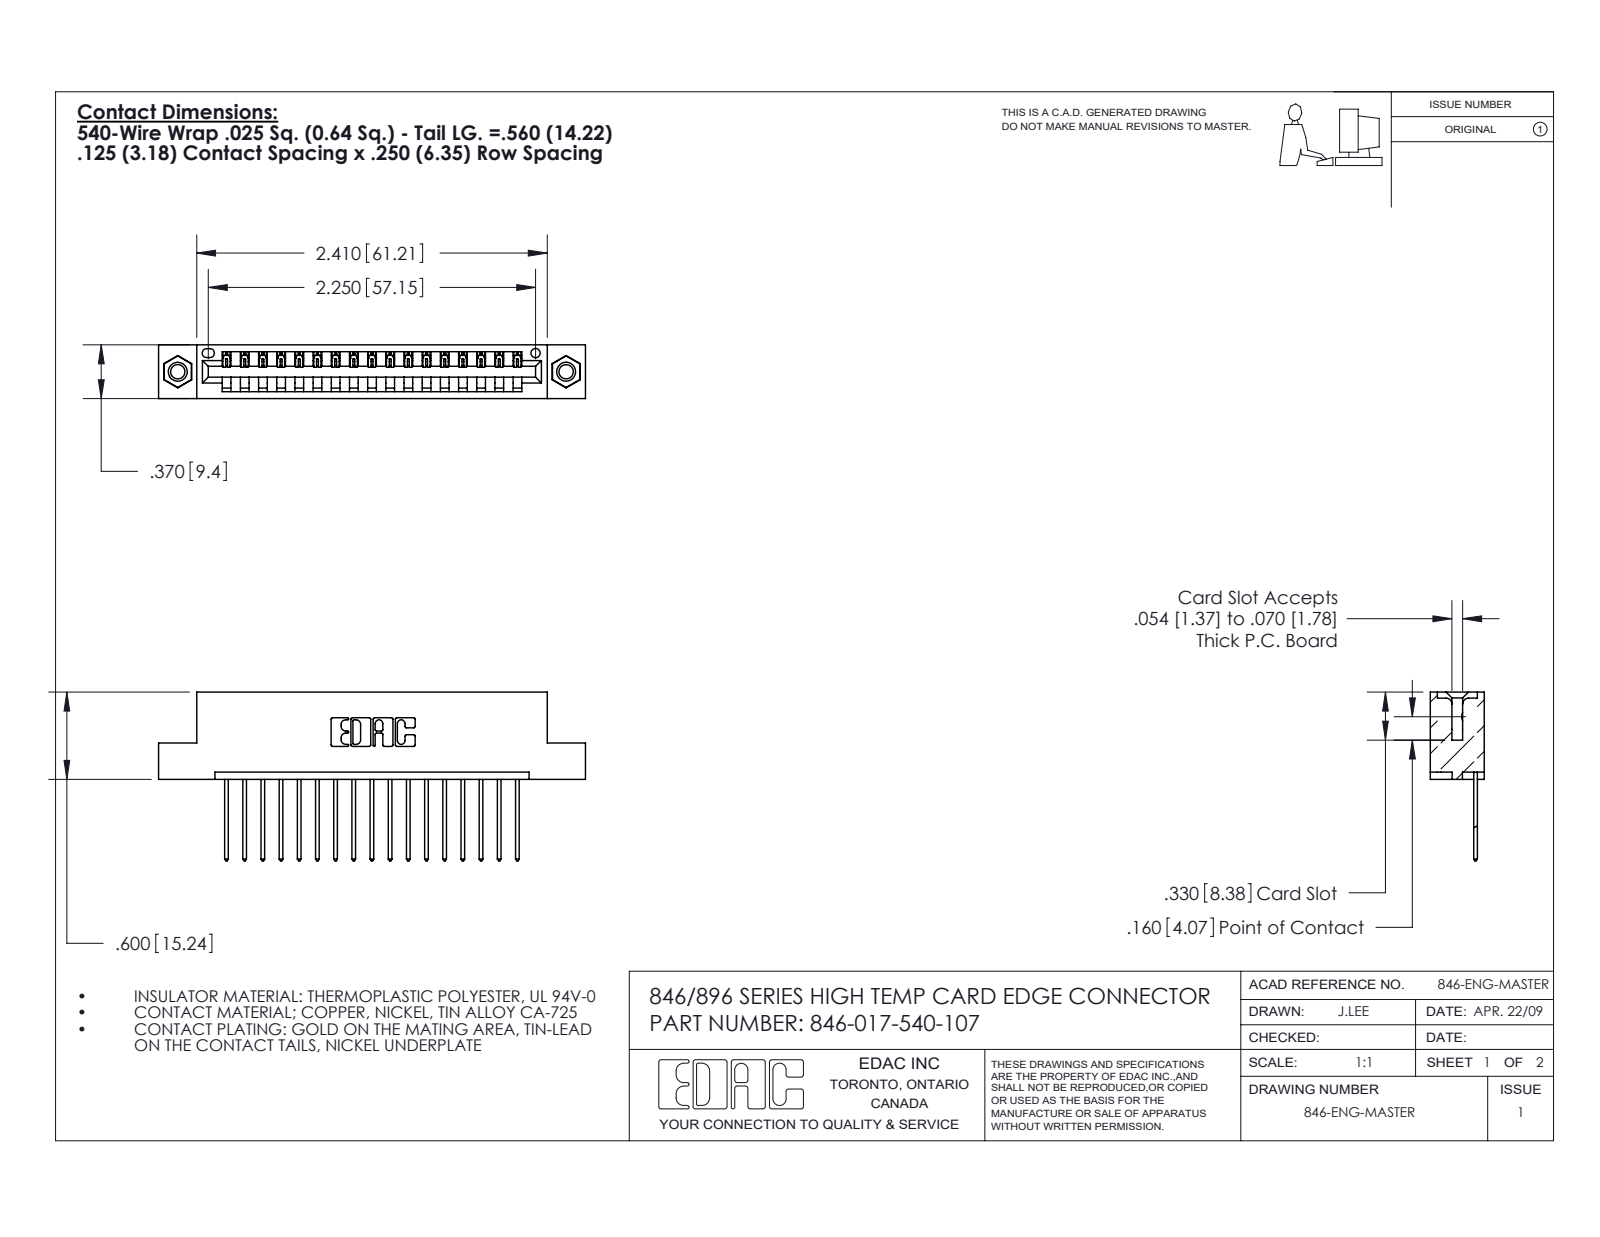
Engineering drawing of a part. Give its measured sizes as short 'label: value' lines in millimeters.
name: 346 Part_Flush Mounting Lugs - 0.156 Dia-TI; 345-292-001_345-293-140; 345-250-001_345-250-005-103; 346-017-540-107
written by: SolidWorks 2016 (CONFIG_CONTROL_DESIGN)
unit: mm
bodies: 20 solids, 1168 faces (788 planar, 364 cylindrical, 16 other)
size: 74.5 × 29.5 × 9.4
volume: 6 980 mm³; area: 8 652 mm²
holes: 2× ⌀2.5, 2× ⌀3.2, 2× ⌀4, 1× ⌀1.6
bosses: 2× ⌀3.9
rounds: 34× R0.2, 34× R0.3, 22× R0.3, 6× R0.2, 6× R0.8, 3× R0.7, 2× R0.8, 2× R1
face distances: 1.2, 8.2, 6.4, 9.4, 1.8, 7.6, 0.6, 3.8, 5.6, 2.5
hole spacings: 6.2, 62.6, 67.8
